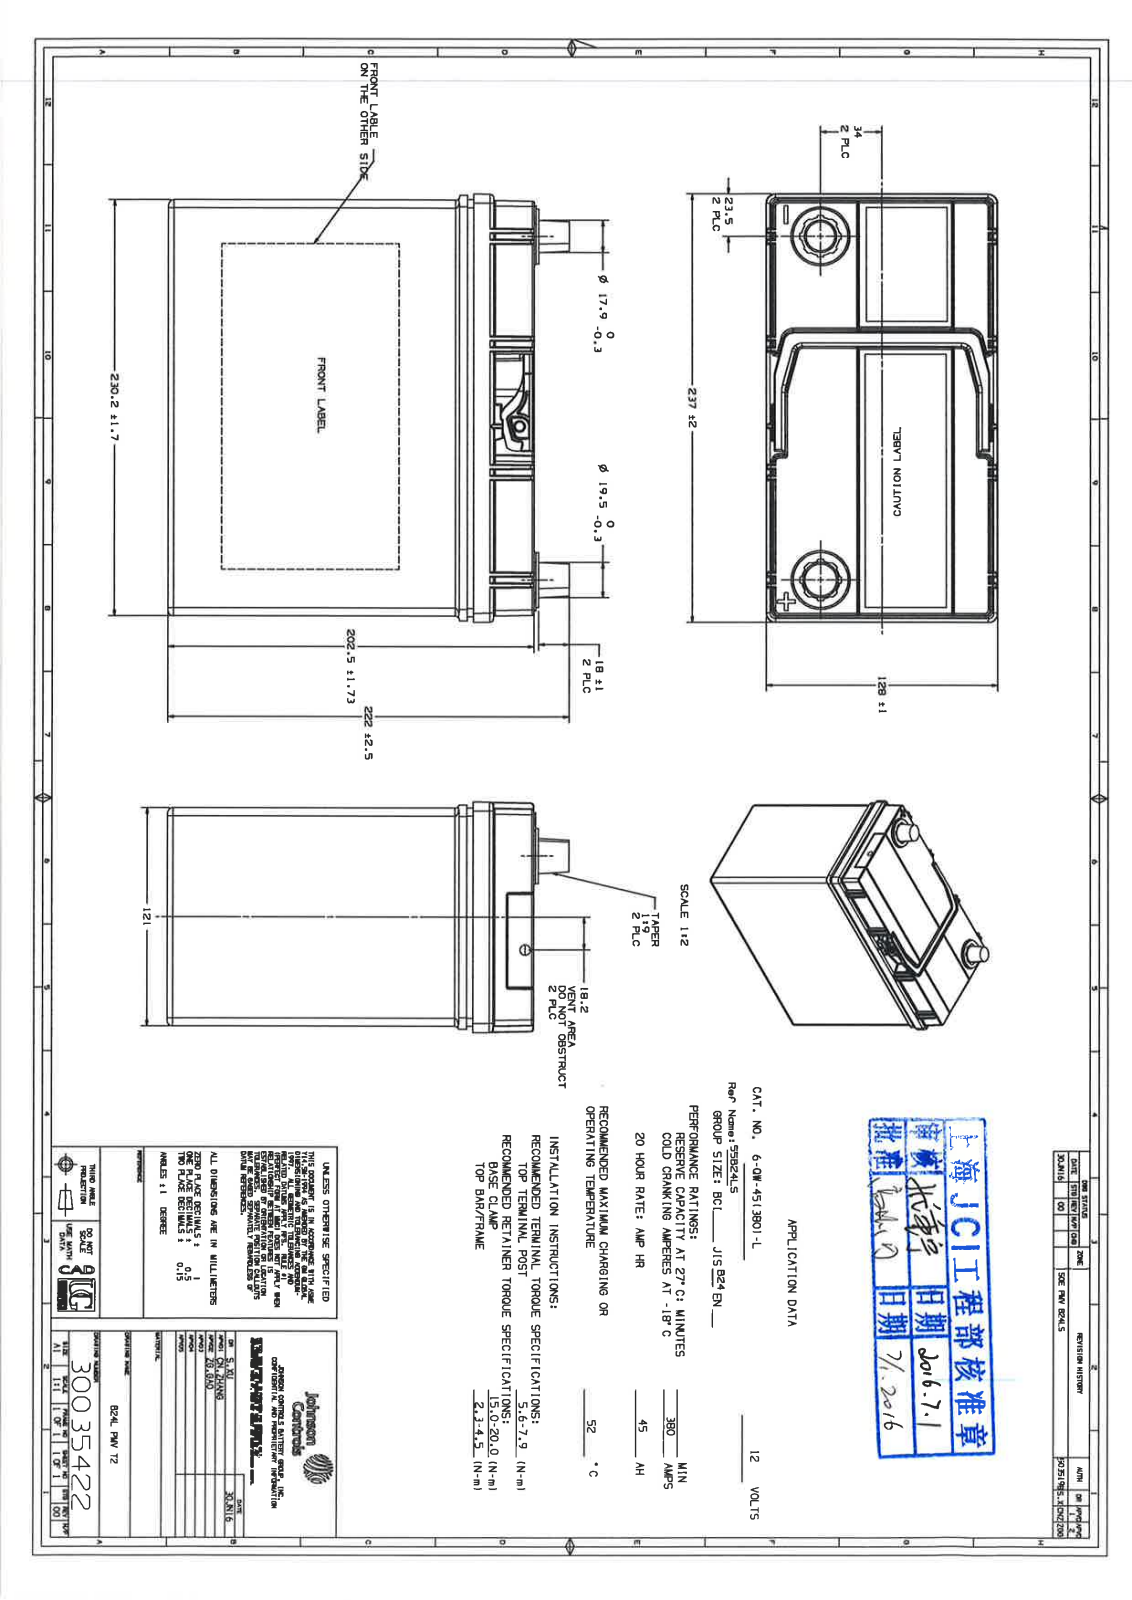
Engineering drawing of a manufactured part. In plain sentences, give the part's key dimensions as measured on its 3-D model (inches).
The part is named "bxusED7Ewvtg". Its 3-D file was written by "EDS PLM SOLUTIONS - UNIGRAPHICS NX 2.0 (AUTOMOTIVE_DESIGN)". It is 14 solids with 7609 faces: 2016 planar, 3045 cylindrical and 2548 other. Overall it measures 9.331 by 8.74 by 5.039 inches. Its volume is 49.03 cubic inches and its surface area 1 158 square inches. Round holes: 6 of diameter 0.75, 1 of diameter 0.228, 1 of diameter 0.411, 1 of diameter 0.803. Round bosses or shafts: 56 of diameter 0.036, 1 of diameter 0.945, 1 of diameter 0.406. Partial cylindrical surfaces (rounded edges, fillets, slot ends): 858 of radius 0.02, 280 of radius 0.012, 199 of radius 0.02, 120 of radius 0.039, 116 of radius 0.03, 52 of radius 0.008, 36 of radius 0.04, 28 of radius 0.118. The main face-to-face distances are 1.502, 4.504, 3.002, 3.004, 1.5, 6.006, 4.764, 7.953, 7.872, 0.08. The hole center spacings are 1.414, 4.506, 2.828, 3.092, 5.92, 1.678, 1.788, 2.278.
